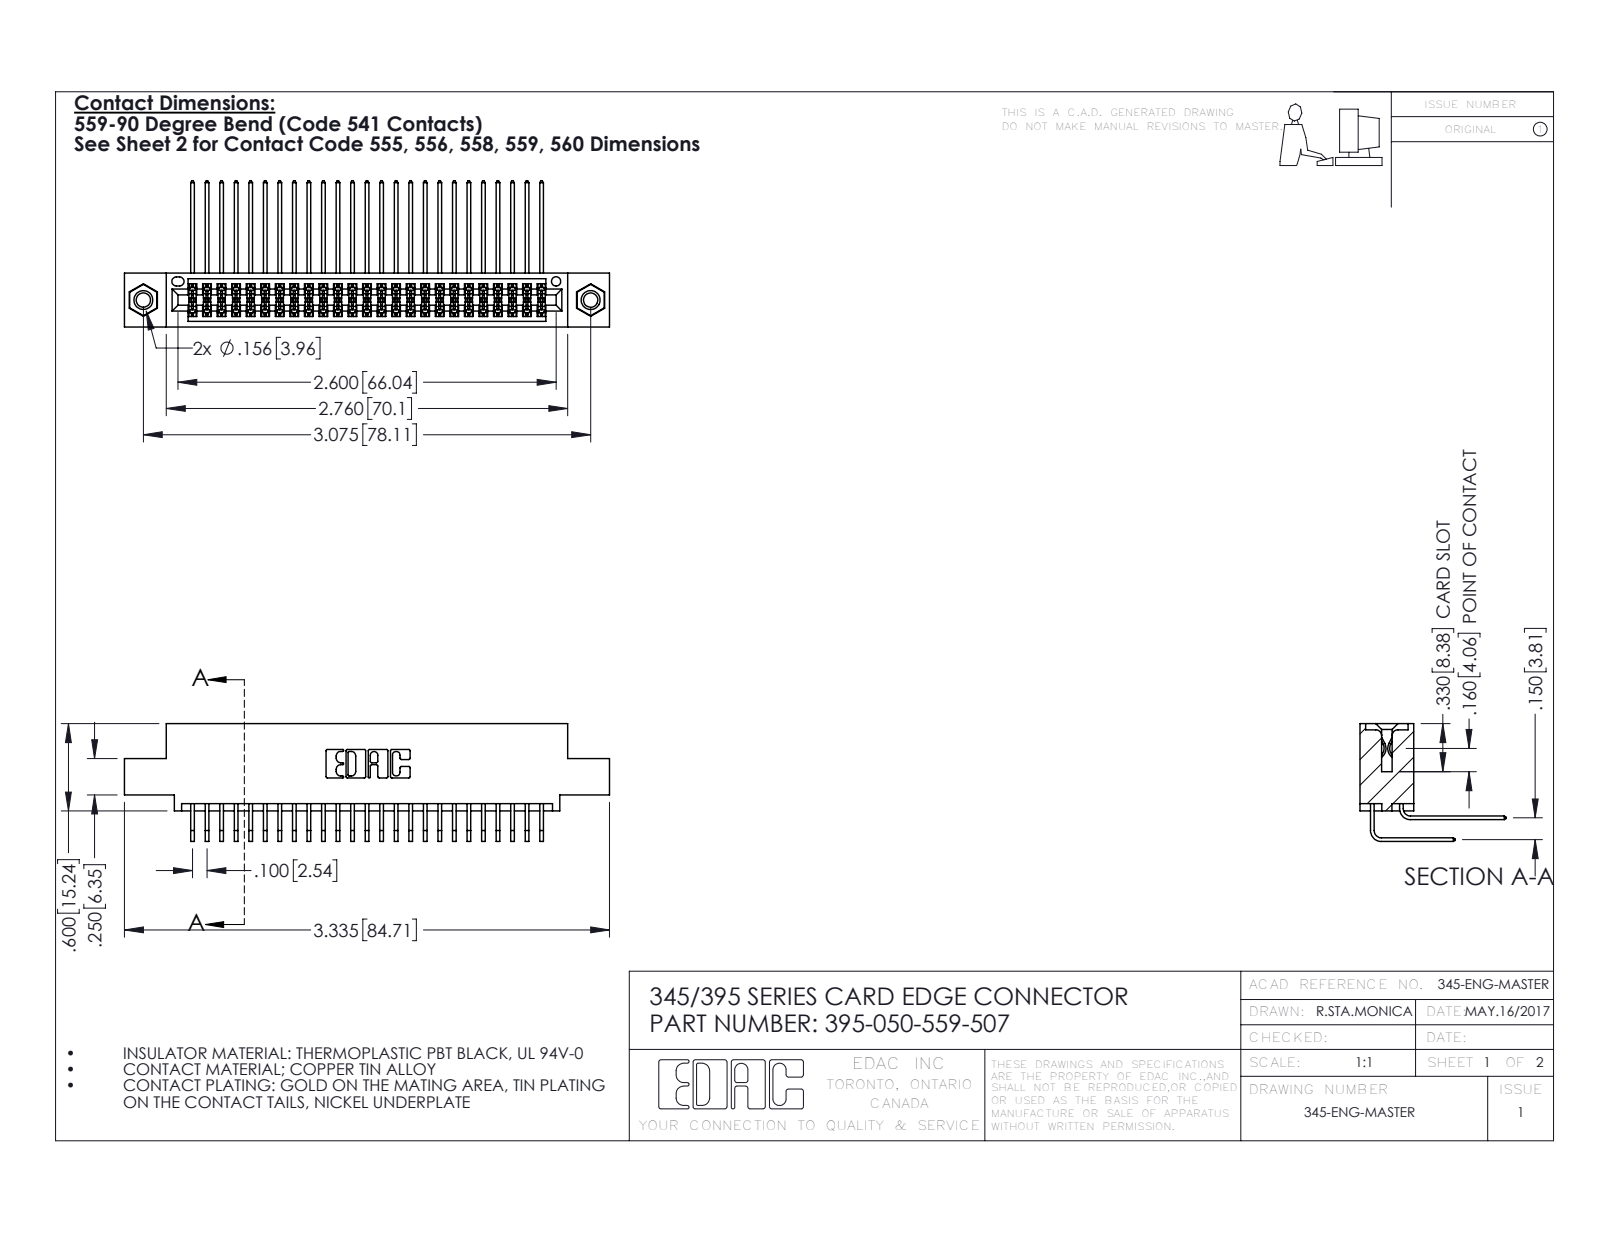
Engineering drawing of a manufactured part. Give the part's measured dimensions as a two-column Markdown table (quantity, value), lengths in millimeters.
| quantity | value |
| --- | --- |
| part name | 395-050-559-507; 345-250-001_345-250-005-103; 345 Part_0.110 Offset - 0.156 Dia-TI; 345-292-001_558 559 Tail - 1 (+1 more) |
| STEP written by | SolidWorks 2016 (CONFIG_CONTROL_DESIGN) |
| units | millimeters |
| bodies | 53 solids, 2790 faces (1866 planar, 908 cylindrical, 16 other) |
| overall size | 84.7 × 25.5 × 20.5 |
| volume | 8 280 mm³ |
| surface area | 13 370 mm² |
| round holes (diameter × count) | 2.5 × 2, 3.2 × 2, 4 × 2, 1.6 × 1 |
| round bosses / shafts (diameter × count) | 3.9 × 2 |
| partial cylindrical surfaces (radius × count) | 0.2 × 75, 0.3 × 22, 0.2 × 6, 0.8 × 6, 0.7 × 3, 0.4 × 2, 0.5 × 2, 0.6 × 2 |
| main face-to-face distances | 1.8, 7.6, 5.1, 9.4, 2.5, 6.9, 0.6, 5.7, 3.8, 4.4 |
| hole center spacings | 6.9, 72.1, 78.1 |
